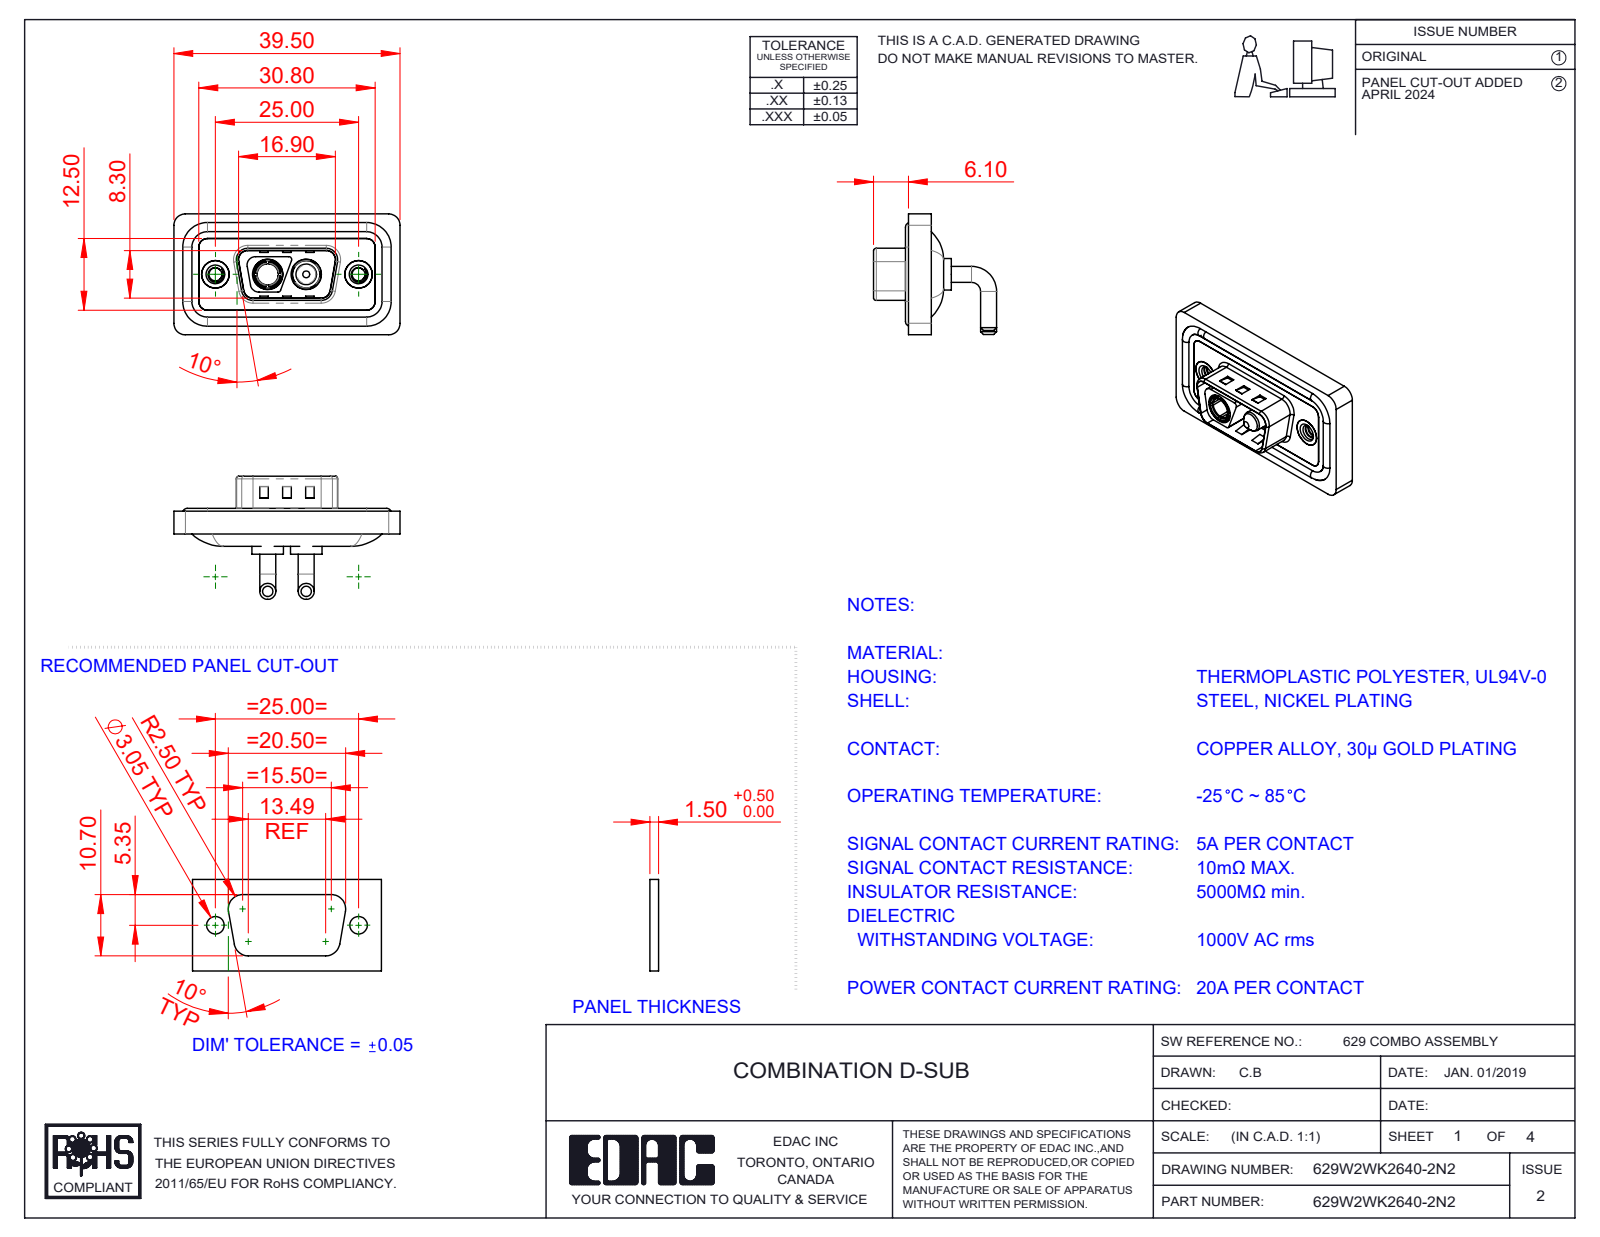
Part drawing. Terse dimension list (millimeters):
name: Power Socket_20A RA; 629Combo Threaded Rivet_2; 629Combo Waterproof Housing_09 Contacts; Power Pin_20A RA (+4 more)
written by: SolidWorks 2023 (CONFIG_CONTROL_DESIGN)
unit: mm
bodies: 11 solids, 542 faces (189 planar, 231 cylindrical, 122 other)
size: 39.5 × 21.5 × 21.1
volume: 4 693 mm³; area: 7 532 mm²
holes: 2× ⌀2.26, 2× ⌀4, 2× ⌀4.8, 2× ⌀4.85, 2× ⌀5, 2× ⌀5.3, 1× ⌀3.7
bosses: 4× ⌀2.8, 4× ⌀1.6, 2× ⌀5.5, 2× ⌀5.2, 2× ⌀4.9, 2× ⌀4.75, 2× ⌀3.75, 1× ⌀4.96
rounds: 20× R1.5, 18× R2, 10× R0.5, 8× R1.6, 4× R0.25, 4× R0.6, 4× R0.65, 4× R0.9
face distances: 0.4, 2.9, 1.1, 0.8, 2.1, 2.5, 3.1, 1.6, 4.5, 1.5
hole spacings: 9.14, 15.86, 6.72, 25
